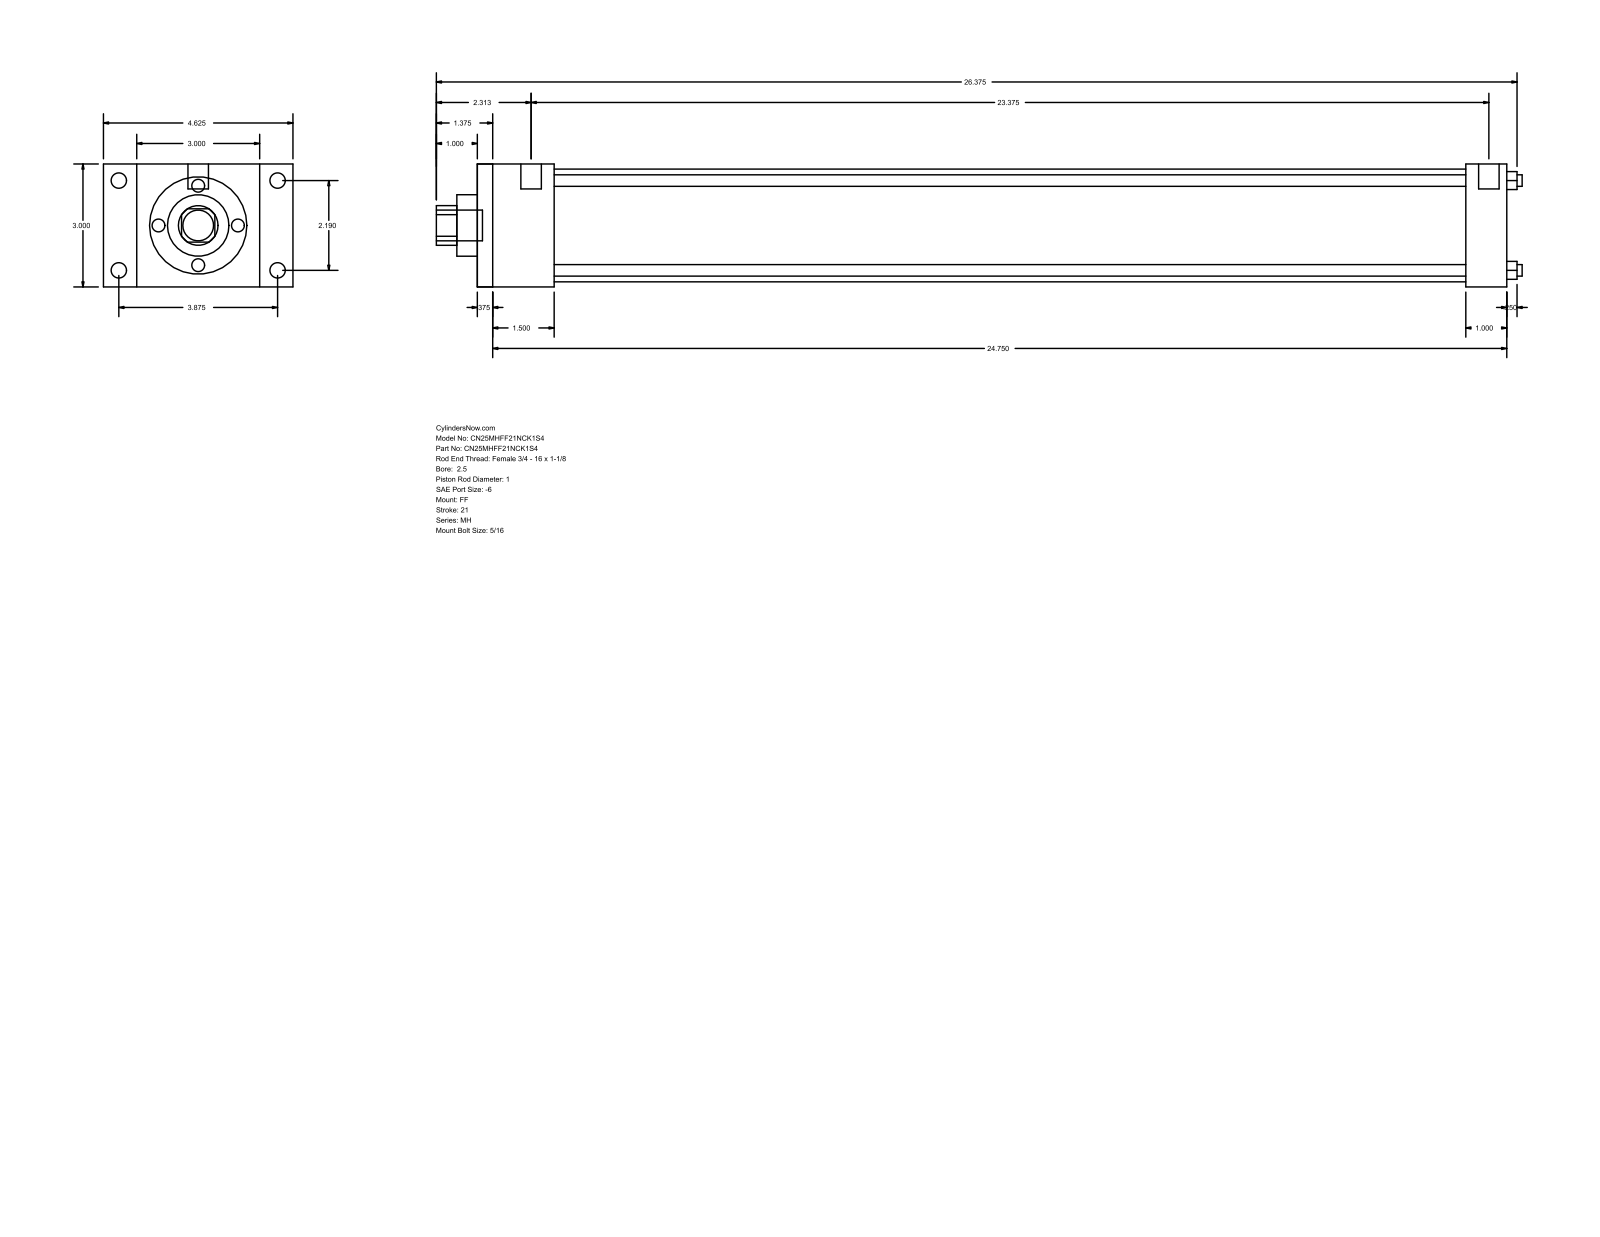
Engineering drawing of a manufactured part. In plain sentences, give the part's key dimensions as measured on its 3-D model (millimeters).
The part is named "MH_FF__0250_1". Its 3-D file was written by "GSSL Pune (CONFIG_CONTROL_DESIGN)". It is 0 solids with 92 faces: 64 planar, 28 cylindrical and 0 other. Overall it measures 673.1 by 117.47 by 76.2 millimeters. Round holes: 4 of diameter 7.14, 1 of diameter 25.4, 1 of diameter 38.1, 1 of diameter 69.85. Round bosses or shafts: 4 of diameter 9.53, 4 of diameter 5.56, 2 of diameter 12.7, 1 of diameter 19.05. Partial cylindrical surfaces (rounded edges, fillets, slot ends): 1 of radius 12.29. The main face-to-face distances are 76.2, 638.18, 9.52, 628.66, 47.63, 612.77, 38.11, 603.25, 565.14, 590.55. The hole center spacings are 39.33, 55.62, 78.66.
